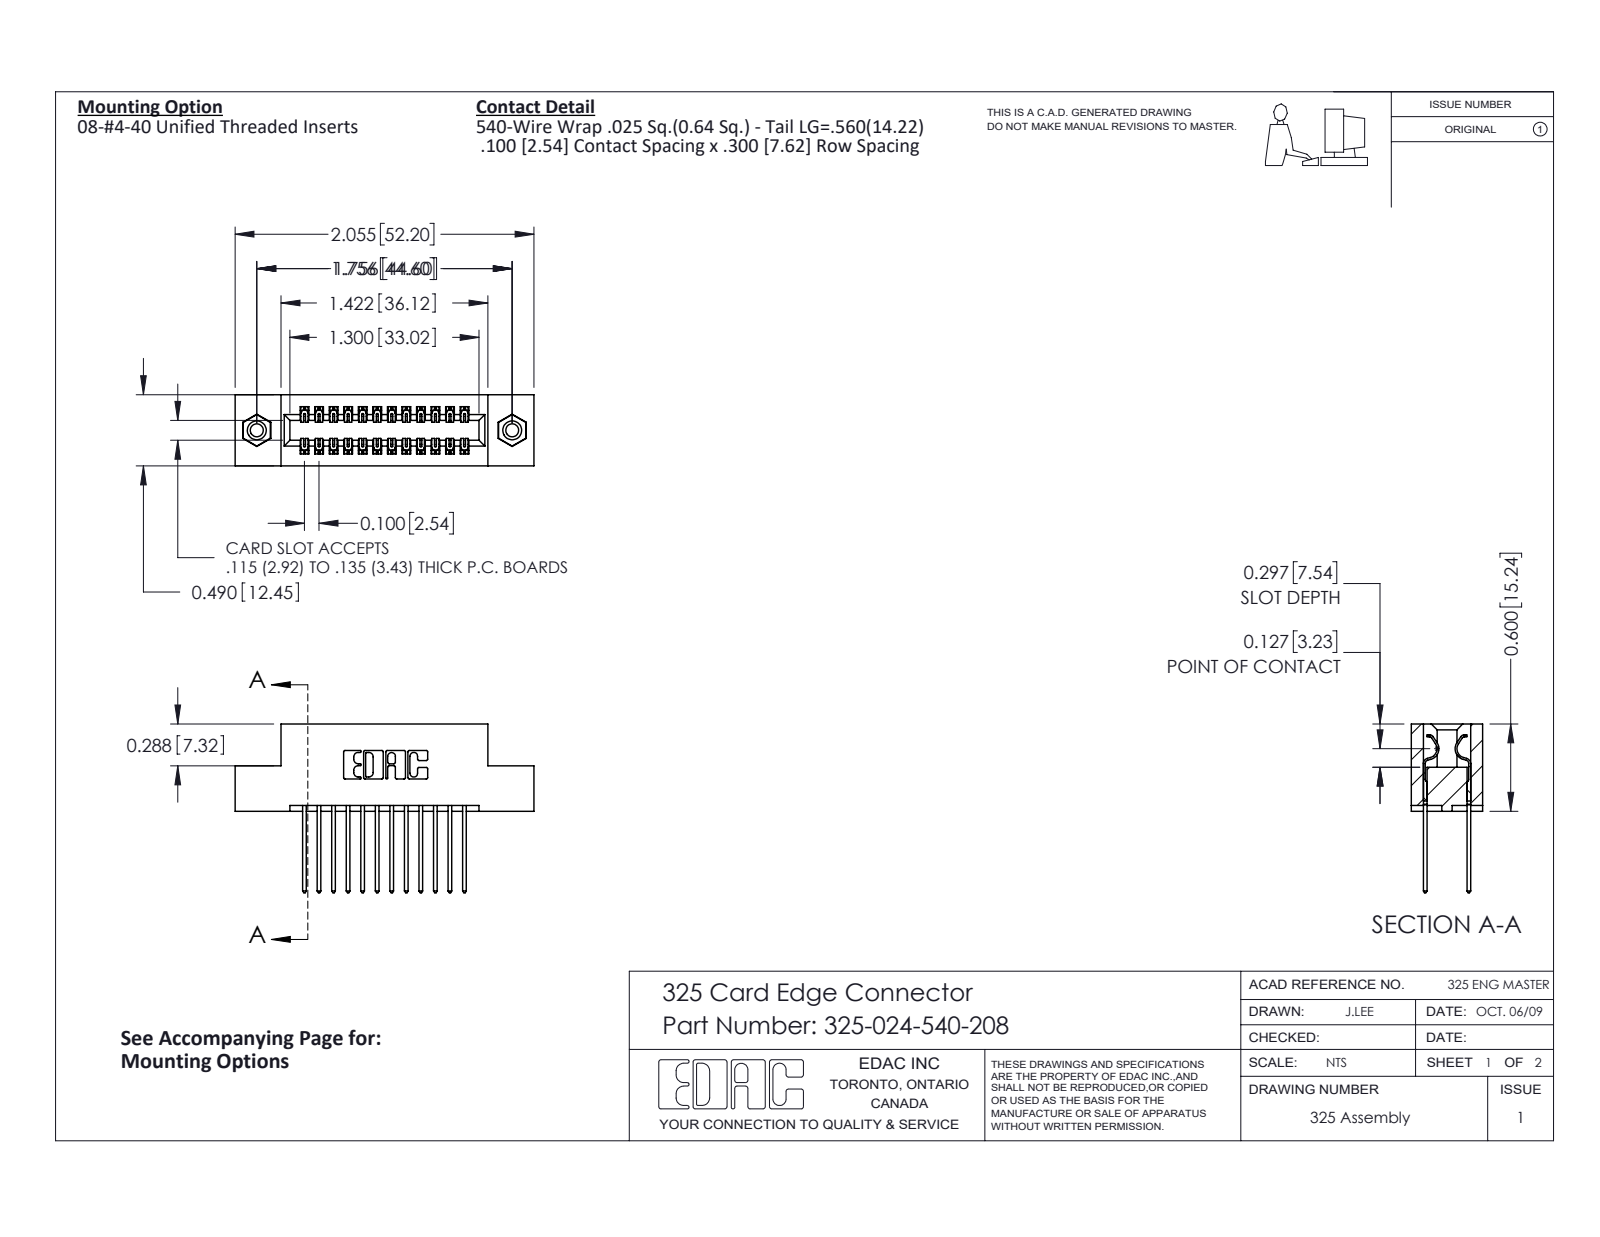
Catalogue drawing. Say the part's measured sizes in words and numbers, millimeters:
The part is named "325-292-001_325-293-140; 345-250-001_345-250-003-102; 325-024-540-208; 325 Part_TI". Its 3-D file was written by "SolidWorks 2016 (CONFIG_CONTROL_DESIGN)". It is 27 solids with 1422 faces: 966 planar, 440 cylindrical and 16 other. Overall it measures 52.2 by 29.5 by 12.4 millimeters. Its volume is 6 550 cubic millimeters and its surface area 7 671 square millimeters. Round holes: 2 of diameter 2.3, 2 of diameter 3.2, 2 of diameter 4.1. Round bosses or shafts: 2 of diameter 3.9. Partial cylindrical surfaces (rounded edges, fillets, slot ends): 36 of radius 0.2, 24 of radius 0.3, 22 of radius 0.3, 6 of radius 0.2, 6 of radius 0.8, 3 of radius 0.7, 2 of radius 0.4, 2 of radius 0.6. The main face-to-face distances are 2.1, 10.3, 7.6, 12.4, 2.7, 9.7, 0.6, 1, 2.5, 8.3. The hole center spacings are 44.6.
